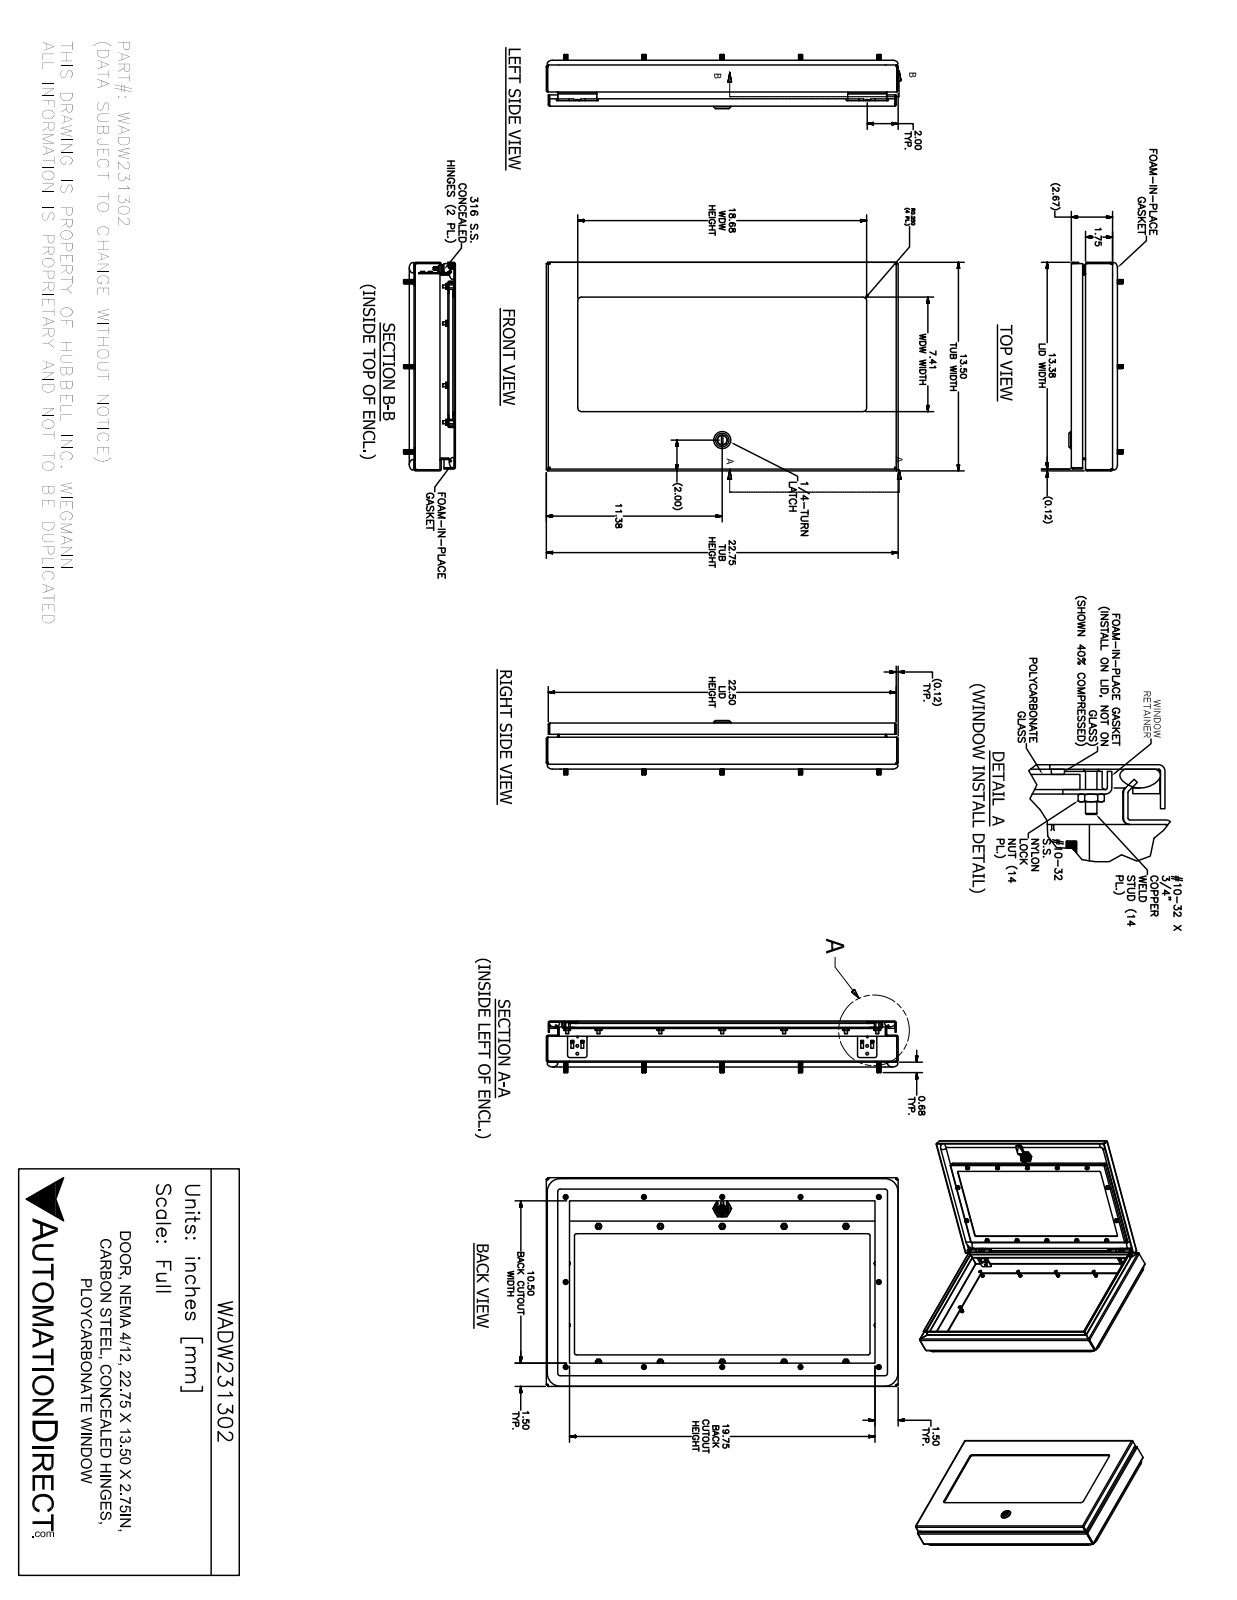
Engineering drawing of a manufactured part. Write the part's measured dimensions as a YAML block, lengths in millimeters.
part_name: "WADW231302"
step_written_by: "SolidWorks 2017 (AUTOMOTIVE_DESIGN)"
units: millimeters
bodies: {solids: 73, faces: 2332, planar: 795, cylindrical: 830, other: 707}
overall_size: [577.9, 342.9, 88.9]
volume: 1819000
surface_area: 1206000
round_holes:
  - {diameter: 4, count: 16}
  - {diameter: 7.1, count: 14}
  - {diameter: 6.3, count: 12}
  - {diameter: 2.4, count: 4}
  - {diameter: 3.9, count: 4}
  - {diameter: 4.2, count: 4}
  - {diameter: 4.4, count: 4}
  - {diameter: 4.8, count: 4}
  - {diameter: 4.7, count: 1}
  - {diameter: 5, count: 1}
  - {diameter: 8, count: 1}
  - {diameter: 10, count: 1}
round_bosses_or_shafts:
  - {diameter: 6.4, count: 34}
  - {diameter: 4.8, count: 14}
  - {diameter: 8.1, count: 12}
  - {diameter: 8, count: 12}
  - {diameter: 4.8, count: 12}
  - {diameter: 9.1, count: 4}
  - {diameter: 8.1, count: 4}
  - {diameter: 6.5, count: 4}
partial_cylinders:
  - {radius: 0.8, count: 34}
  - {radius: 0.3, count: 30}
  - {radius: 1.3, count: 26}
  - {radius: 2.7, count: 24}
  - {radius: 3.2, count: 20}
  - {radius: 0.4, count: 18}
  - {radius: 0.5, count: 13}
  - {radius: 0.8, count: 8}
face_to_face_distances: [1.9, 65.9, 8.6, 10.4, 6.4, 2.2, 4.1, 55.4, 57.3, 63.7]
hole_center_spacings: [307.6, 128.6, 379.7, 101.6, 279.4, 476.1, 139.7, 189.9]
